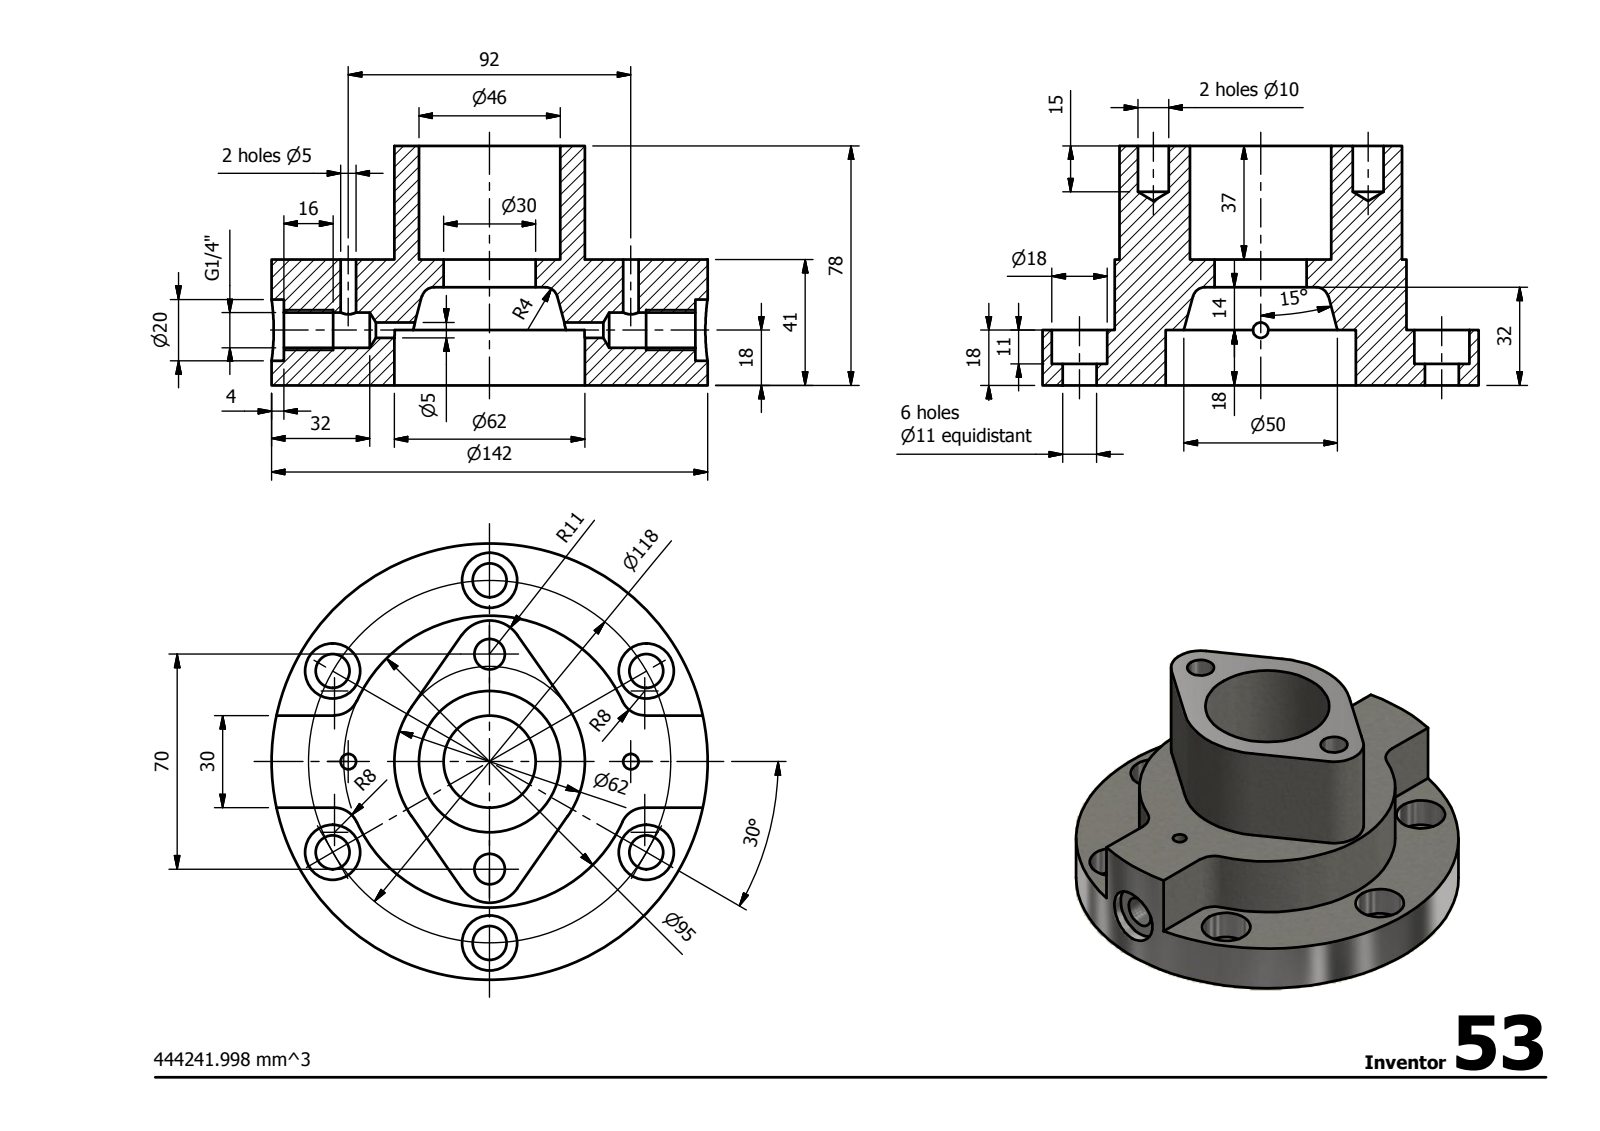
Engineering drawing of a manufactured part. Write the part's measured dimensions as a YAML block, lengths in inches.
step_written_by: "Autodesk Inventor 2014 (AUTOMOTIVE_DESIGN)"
units: inches
bodies: {solids: 1, faces: 67, planar: 25, cylindrical: 36, other: 6}
overall_size: [5.591, 5.591, 3.071]
volume: 27.11
surface_area: 116.5
round_holes:
  - {diameter: 0.433, count: 6}
  - {diameter: 0.709, count: 6}
  - {diameter: 0.197, count: 3}
  - {diameter: 0.394, count: 2}
  - {diameter: 0.451, count: 1}
  - {diameter: 0.787, count: 1}
  - {diameter: 1.181, count: 1}
  - {diameter: 1.811, count: 1}
round_bosses_or_shafts:
  - {diameter: 5.591, count: 1}
  - {diameter: 2.441, count: 1}
partial_cylinders:
  - {radius: 0.315, count: 4}
  - {radius: 0.433, count: 2}
  - {radius: 1.87, count: 1}
face_to_face_distances: [0.709, 1.614, 0.906, 3.071, 2.362, 1.457, 2.441, 2.44, 0.276, 0.433]
hole_center_spacings: [2.323, 1.179, 2.024, 2.276, 2.945, 3.24, 3.995, 4.023]
